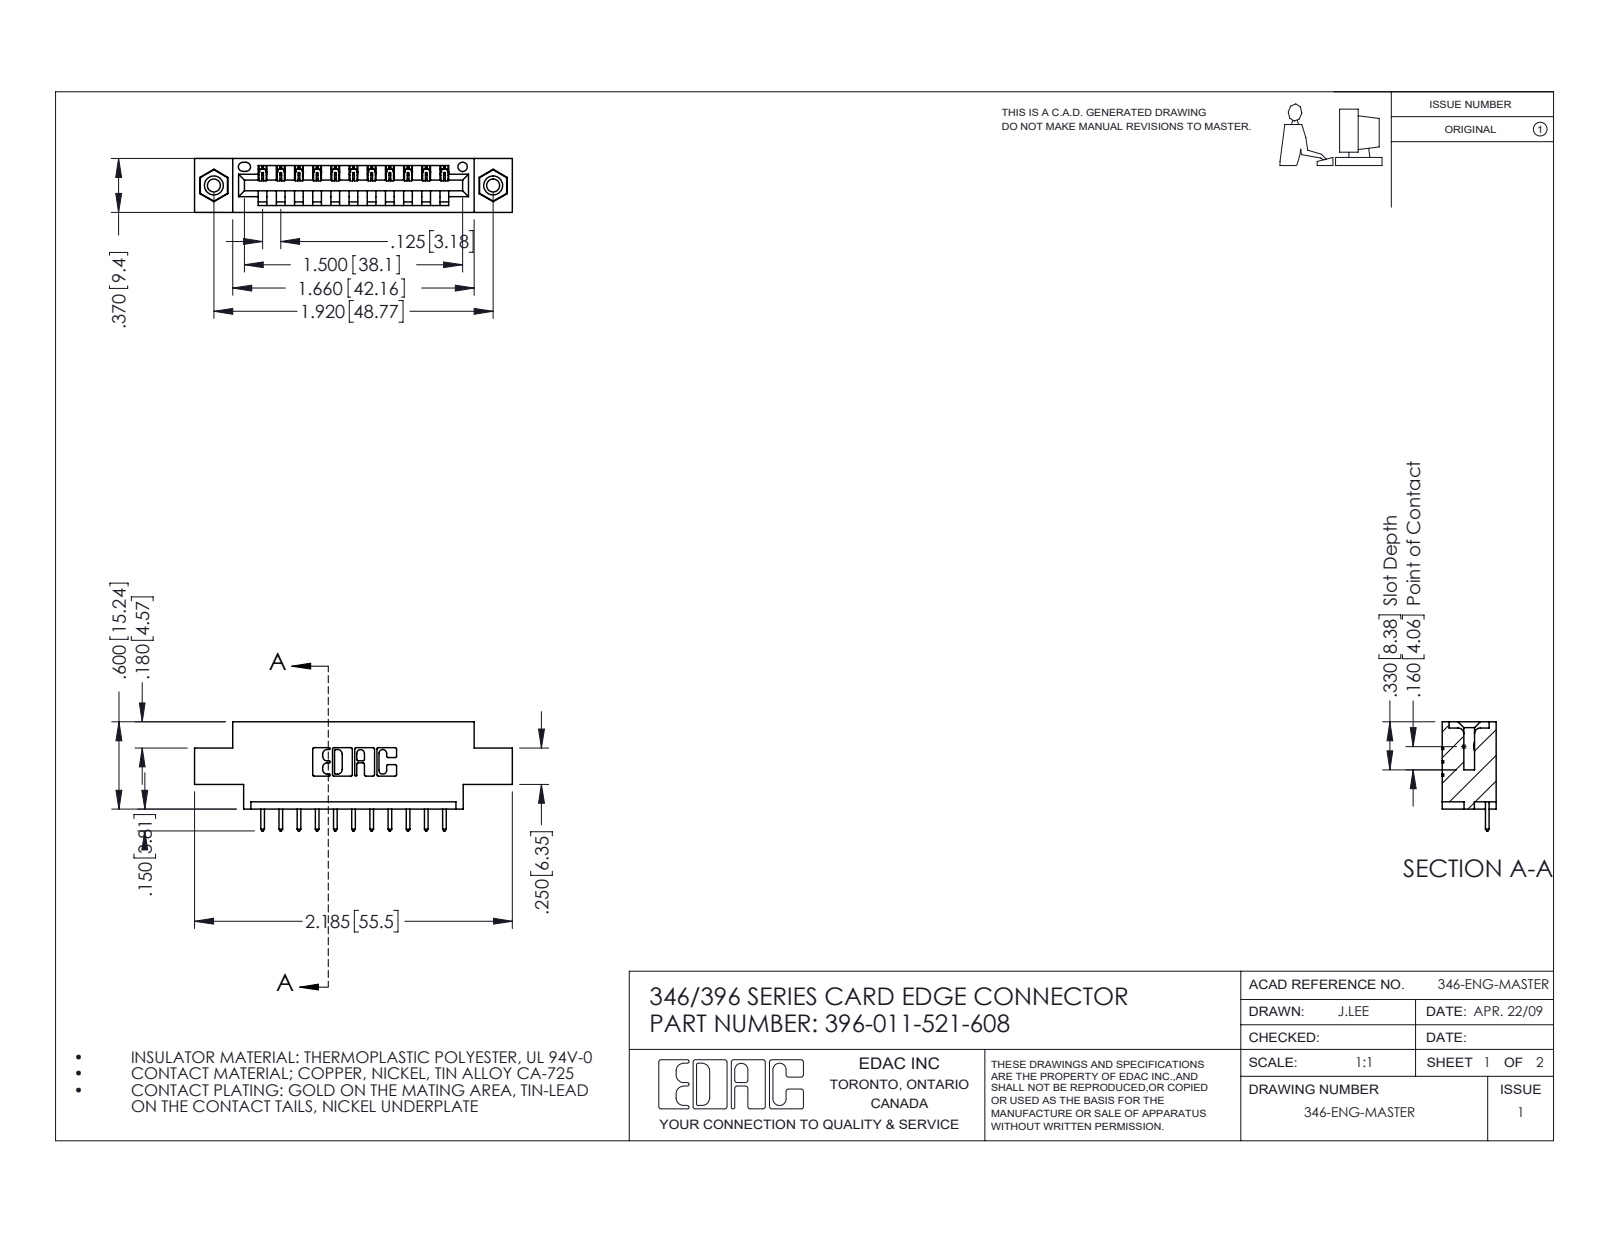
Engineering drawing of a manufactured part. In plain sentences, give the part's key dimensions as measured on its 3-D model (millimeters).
The part is named "346 Part_0.170 Offset - 0.156 Dia-TI; 396-011-521-608; 345-250-001_345-250-003-102; 345-292-001_345-293-121". Its 3-D file was written by "SolidWorks 2016 (CONFIG_CONTROL_DESIGN)". It is 14 solids with 824 faces: 552 planar, 256 cylindrical and 16 other. Overall it measures 55.5 by 19.1 by 9.4 millimeters. Its volume is 4 900 cubic millimeters and its surface area 5 855 square millimeters. Round holes: 2 of diameter 2.3, 2 of diameter 3.2, 2 of diameter 4, 1 of diameter 1.6. Round bosses or shafts: 2 of diameter 3.9. Partial cylindrical surfaces (rounded edges, fillets, slot ends): 22 of radius 0.2, 22 of radius 0.3, 22 of radius 0.3, 6 of radius 0.2, 6 of radius 0.8, 3 of radius 0.7, 2 of radius 0.8, 2 of radius 1. The main face-to-face distances are 6.4, 9.4, 1.2, 8.2, 5.6, 3.8, 2.5, 4.4, 1.8, 7.6. The hole center spacings are 6.2, 43.6, 48.8.
